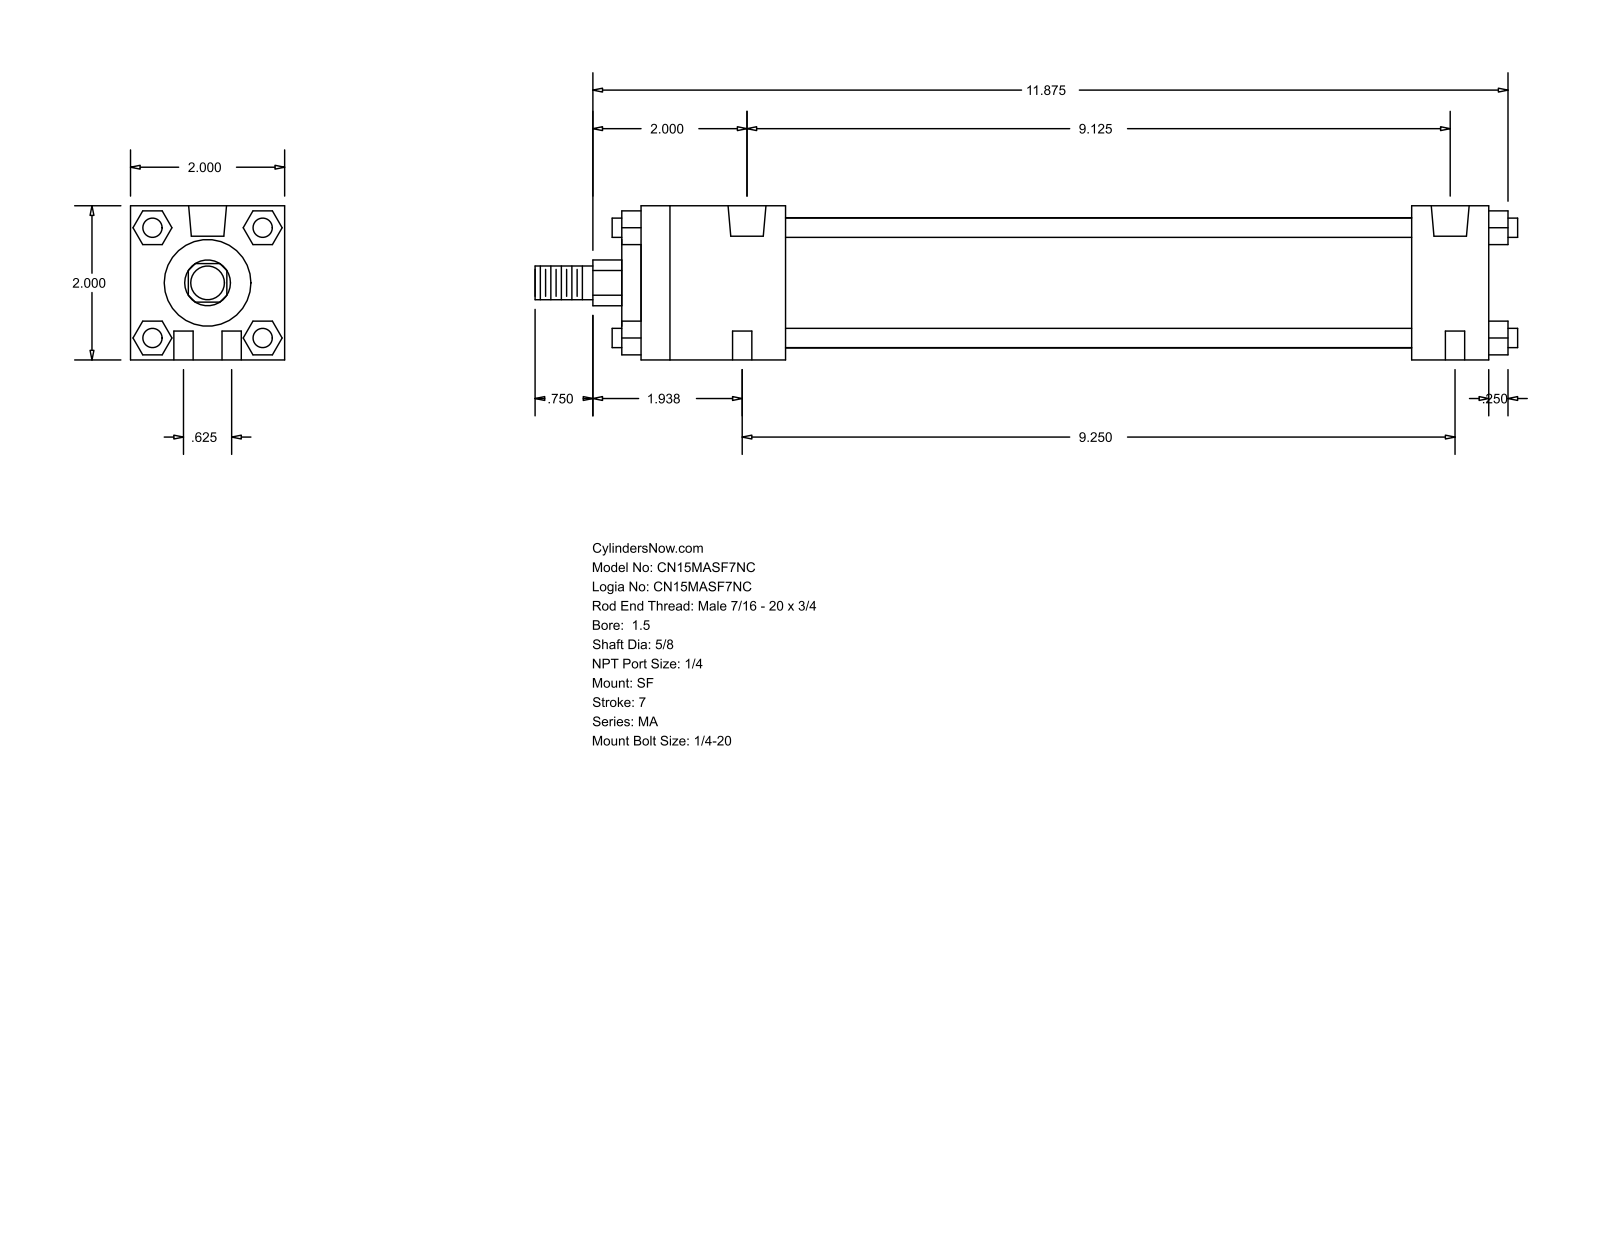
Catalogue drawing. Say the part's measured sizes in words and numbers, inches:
The part is named "MA_SF__0150_0.625". Its 3-D file was written by "GSSL Pune (CONFIG_CONTROL_DESIGN)". It is 0 solids with 124 faces: 94 planar, 30 cylindrical and 0 other. Overall it measures 12.75 by 2 by 2 inches. Round holes: 4 of diameter 0.25, 2 of diameter 0.313, 2 of diameter 0.492. Round bosses or shafts: 4 of diameter 0.25, 1 of diameter 1.69, 1 of diameter 1.125, 1 of diameter 0.625, 1 of diameter 0.437. Partial cylindrical surfaces (rounded edges, fillets, slot ends): 1 of radius 0.297. The main face-to-face distances are 2, 11, 0.25, 11.25, 1.875, 10, 8.125, 9.125, 1, 2.125. The hole center spacings are 0.319, 9.193, 0.625, 9.125, 9.25, 9.271.
